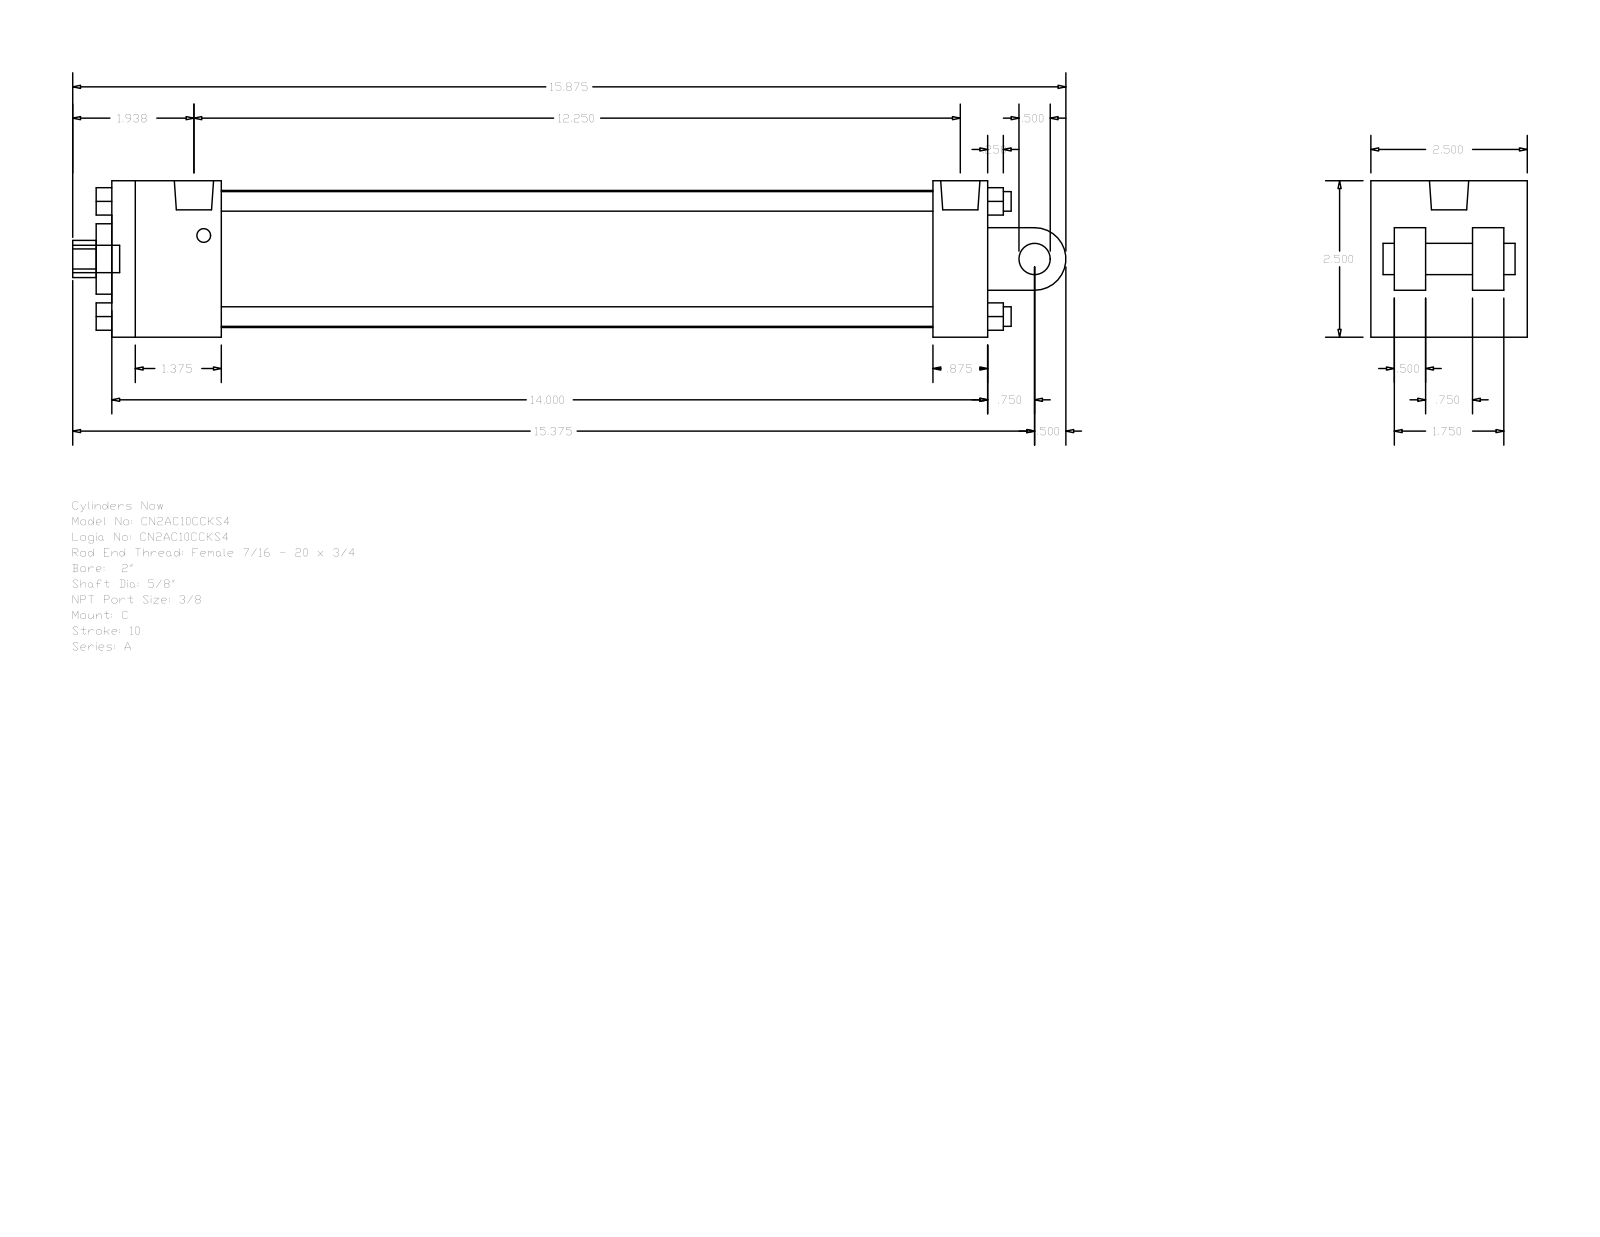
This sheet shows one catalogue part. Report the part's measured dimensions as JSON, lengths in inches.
{"part_name": "A_C__0200_0.625", "step_written_by": "GSSL Pune (CONFIG_CONTROL_DESIGN)", "units": "inches", "bodies": {"solids": 0, "faces": 135, "planar": 102, "cylindrical": 33, "other": 0}, "overall_size": [15.875, 2.5, 2.5], "round_holes": [[0.219, 2], [0.625, 1], [0.627, 1], [1.125, 1], [2.19, 1]], "round_bosses_or_shafts": [[0.313, 4], [0.219, 2], [0.627, 1], [0.5, 1], [0.437, 1]], "partial_cylinders_radius": [[0.297, 1], [0.5, 1]], "face_to_face_distances": [2.5, 14, 1.75, 0.375, 12.25, 13.125, 11.375, 0.875, 0.5, 1.625], "hole_center_spacings": [0.156]}
